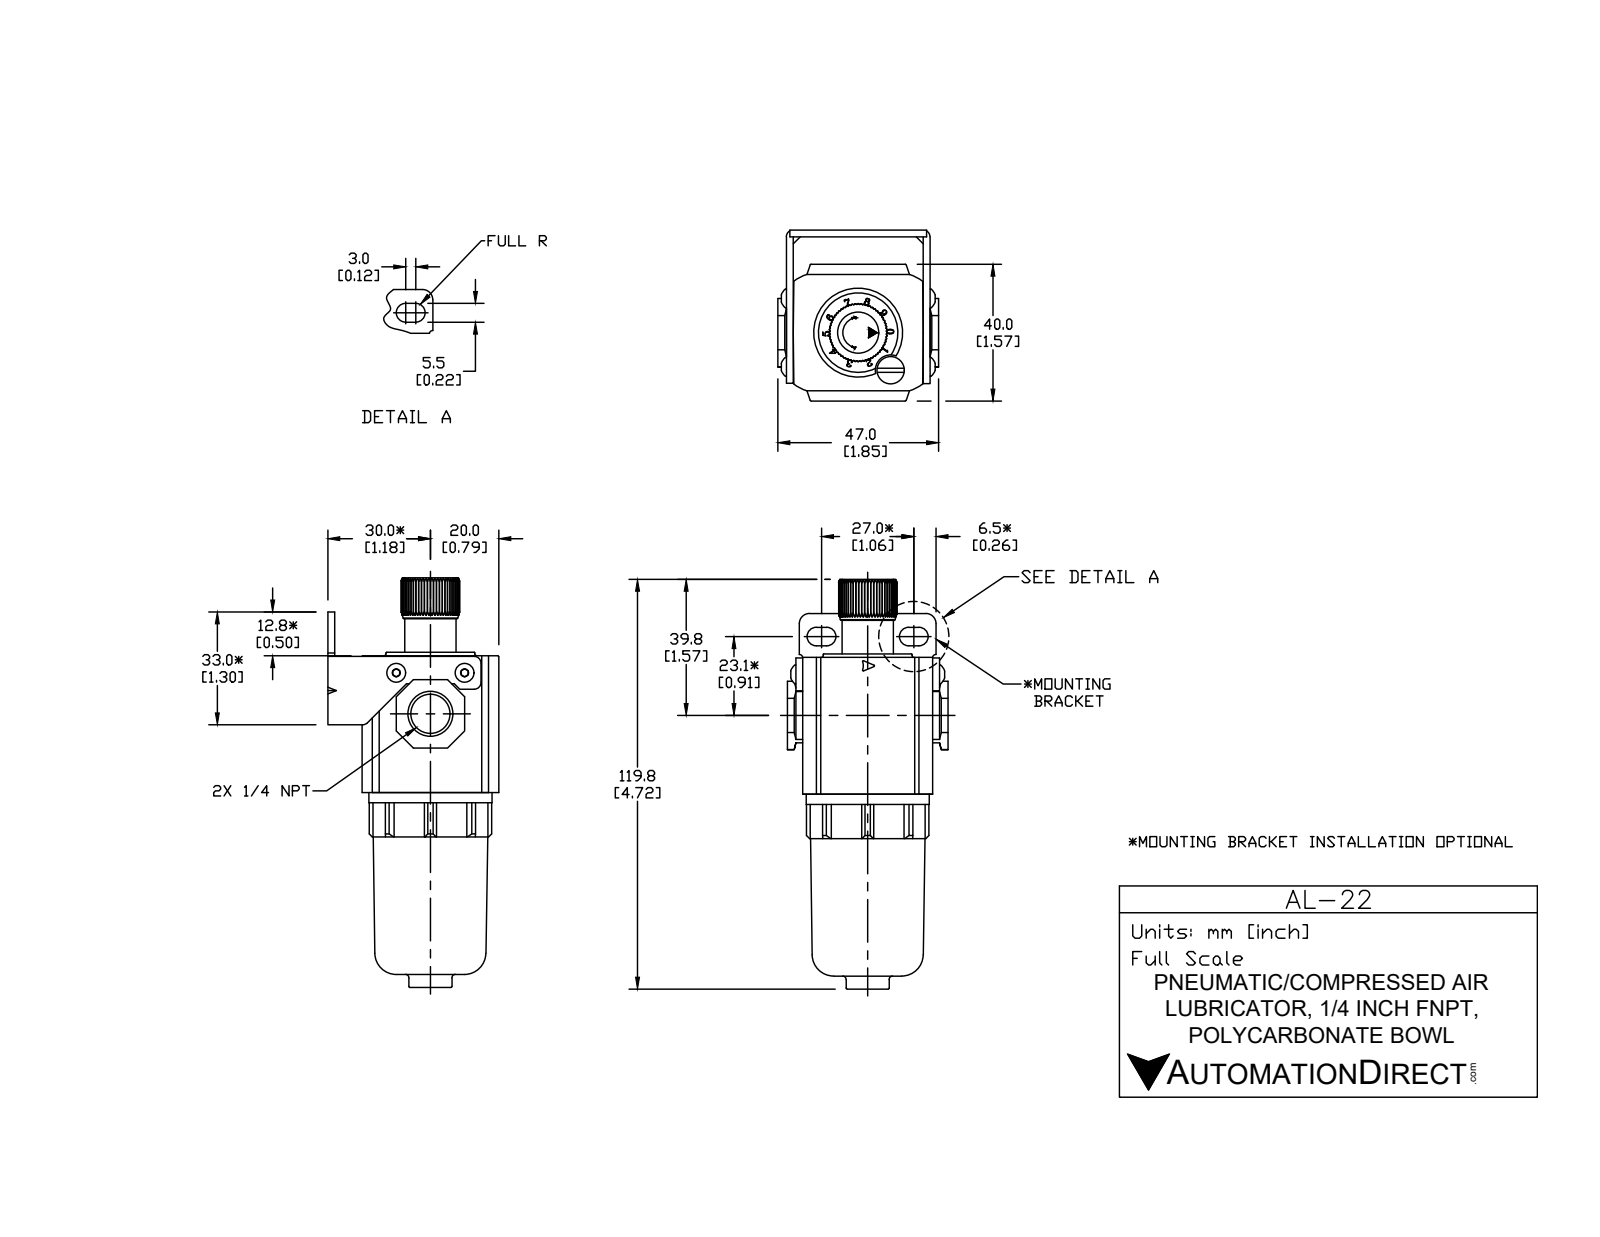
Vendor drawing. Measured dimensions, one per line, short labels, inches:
name: AL-22
written by: SolidWorks 2015 (CONFIG_CONTROL_DESIGN)
unit: in
bodies: 7 solids, 508 faces (299 planar, 97 cylindrical, 112 other)
size: 4.677 × 1.969 × 1.85
volume: 5.505 in³; area: 45.38 in²
holes: 2× ⌀0.134, 1× ⌀0.438, 1× ⌀0.976, 1× ⌀0.984
bosses: 1× ⌀1.417, 1× ⌀1.339, 1× ⌀1.024, 1× ⌀0.591, 1× ⌀0.496
rounds: 5× R0.079, 4× R0.012, 4× R0.106, 4× R0.472, 2× R0.118, 2× R0.157, 1× R0.335, 1× R0.665
face distances: 1.575, 0.079, 1.496, 0.394, 1.969, 0.315, 1.89, 1.654, 0.177, 0.039
hole spacings: 0.615, 0.787
